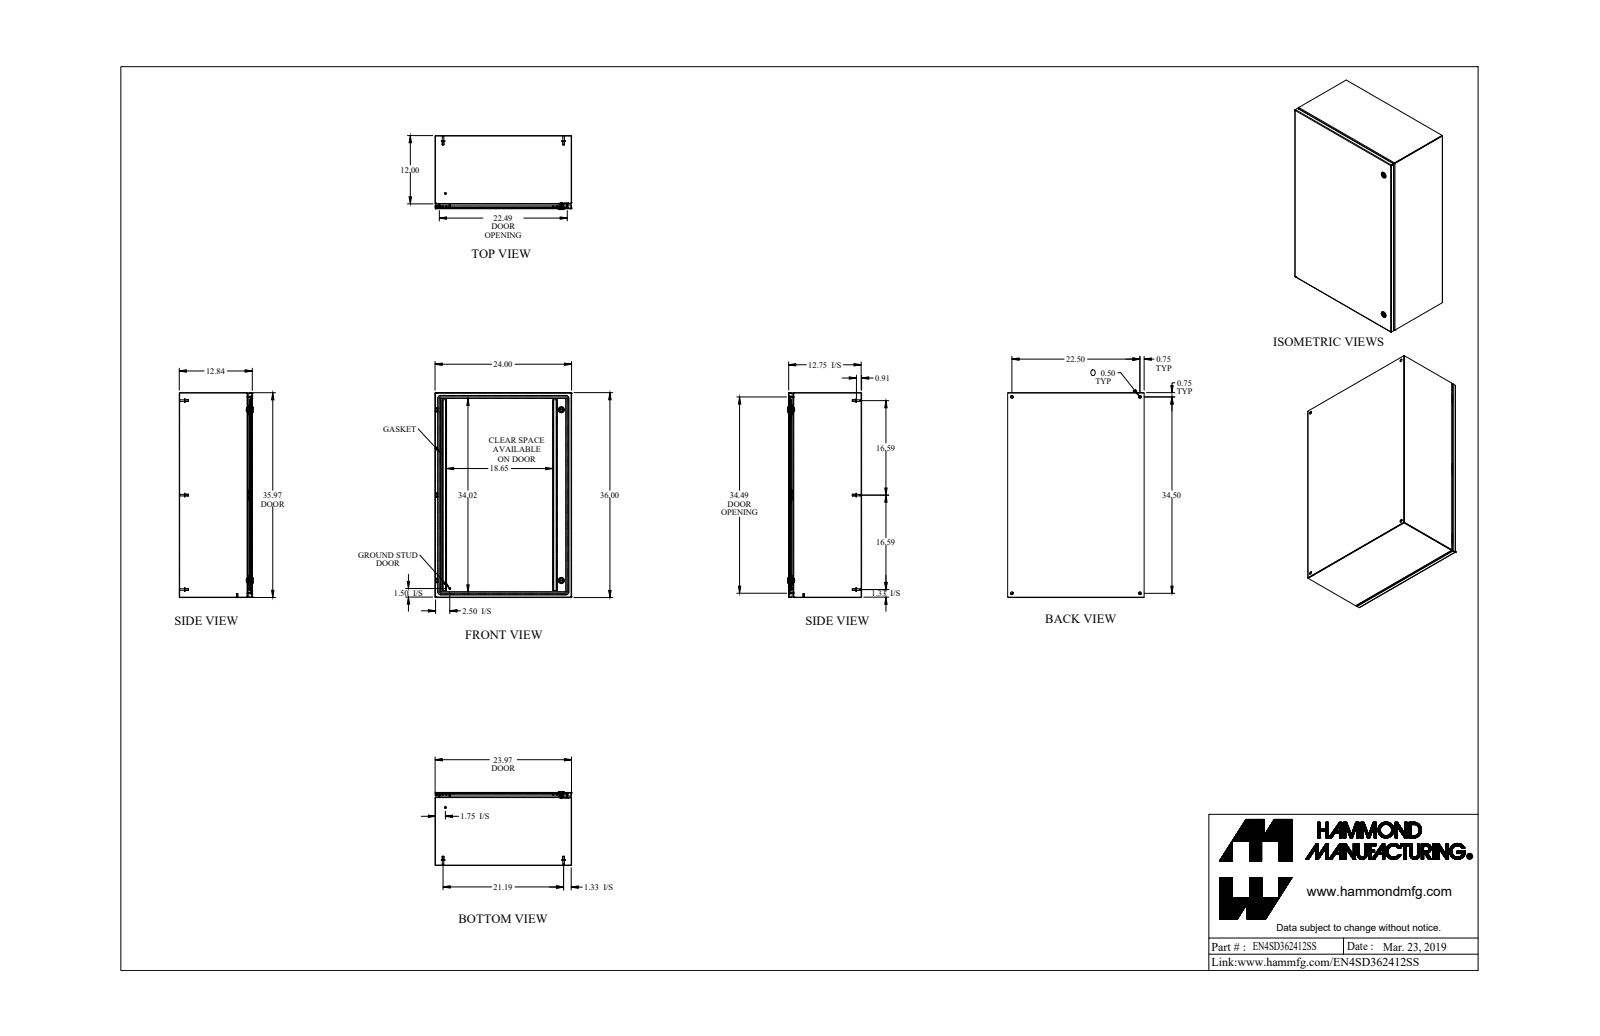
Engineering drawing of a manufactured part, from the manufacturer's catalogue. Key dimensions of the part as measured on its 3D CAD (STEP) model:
Part name (STEP PRODUCT): EN4SD362412SS
STEP written by: SolidWorks 2019 (AUTOMOTIVE_DESIGN)
Units: inches
Bodies: 37 solids, 943 faces (454 planar, 309 cylindrical, 180 other)
Overall size (bounding box): 36 × 24 × 13.002
Volume: 261.2 in³ · Surface area: 7 341 in²
Round holes (diameter × count): ⌀0.5 ×6, ⌀0.197 ×2, ⌀0.387 ×2, ⌀0.63 ×2, ⌀0.768 ×2, ⌀0.172 ×1, ⌀0.24 ×1, ⌀0.242 ×1
Round bosses / shafts (diameter × count): ⌀0.625 ×8, ⌀0.313 ×8, ⌀0.275 ×6, ⌀1.1 ×2, ⌀0.785 ×2, ⌀0.525 ×2, ⌀0.25 ×2, ⌀0.236 ×2
Partial cylindrical surfaces — rounded edges, fillets, slot ends (radius × count): R0.036 ×18, R0.108 ×18, R0.01 ×12, R0.048 ×12, R0.312 ×12, R0.006 ×6, R0.062 ×6, R0.125 ×4
Main face-to-face distances: 0.072, 12.77, 12.698, 12.842, 23.928, 35.928, 23.856, 24, 35.856, 36
Hole centre spacings: 21.557, 22.5, 34.5, 41.189, 2.488, 2.489, 29.999, 32.266
